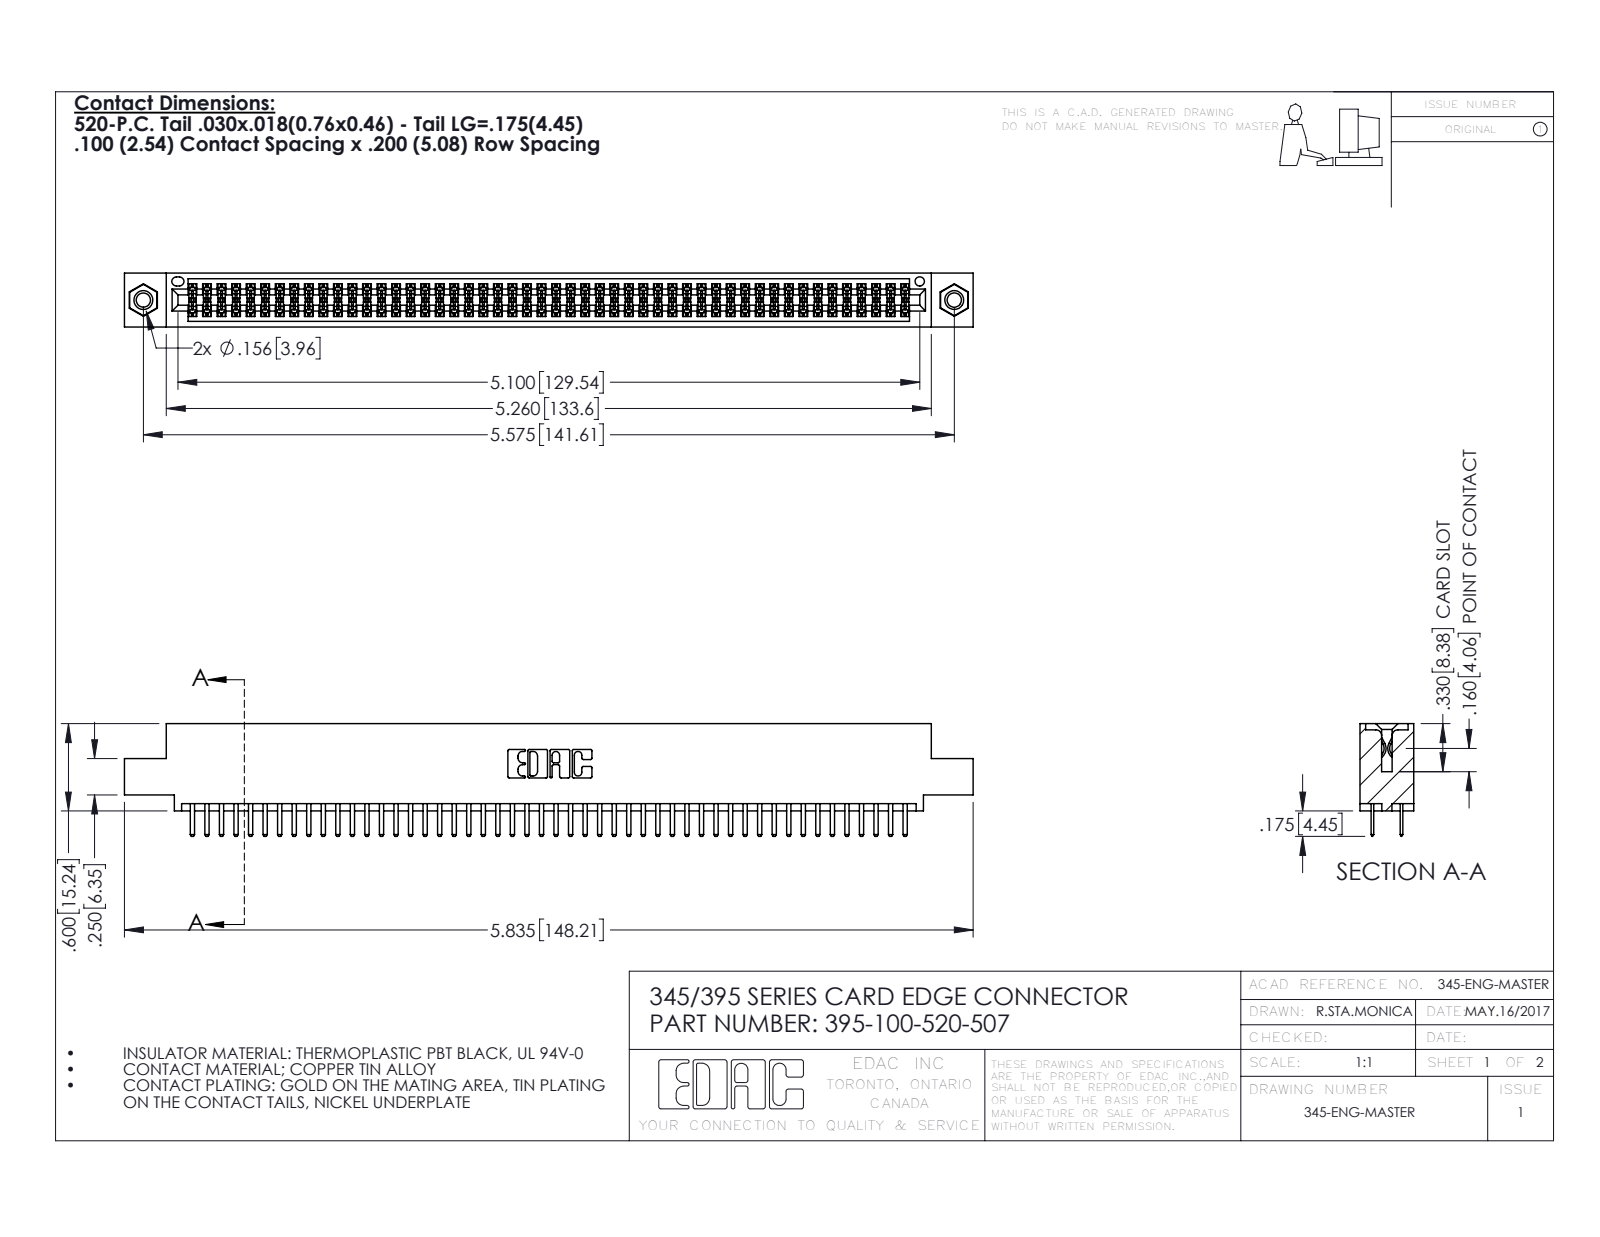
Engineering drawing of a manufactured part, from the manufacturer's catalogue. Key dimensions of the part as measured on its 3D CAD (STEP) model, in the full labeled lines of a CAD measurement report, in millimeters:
Part name (STEP PRODUCT): 345 Part_0.110 Offset - 0.156 Dia-TI; 345-292-001_345-293-120; 345-250-001_345-250-005-103; 395-100-520-507
STEP written by: SolidWorks 2016 (CONFIG_CONTROL_DESIGN)
Units: millimetres
Bodies: 103 solids, 5590 faces (3616 planar, 1958 cylindrical, 16 other)
Overall size (bounding box): 148.2 × 19.7 × 9.4
Volume: 14 300 mm³ · Surface area: 21 380 mm²
Round holes (diameter × count): ⌀2.5 ×2, ⌀3.2 ×2, ⌀4 ×2, ⌀1.6 ×1
Round bosses / shafts (diameter × count): ⌀3.9 ×2
Partial cylindrical surfaces — rounded edges, fillets, slot ends (radius × count): R0.2 ×150, R0.3 ×104, R0.3 ×22, R0.2 ×6, R0.8 ×6, R0.7 ×3, R0.4 ×2, R0.5 ×2
Main face-to-face distances: 1.8, 7.6, 5.1, 9.4, 2.5, 6.9, 0.6, 5.7, 0.6, 1.8
Hole centre spacings: 6.9, 135.6, 141.6
